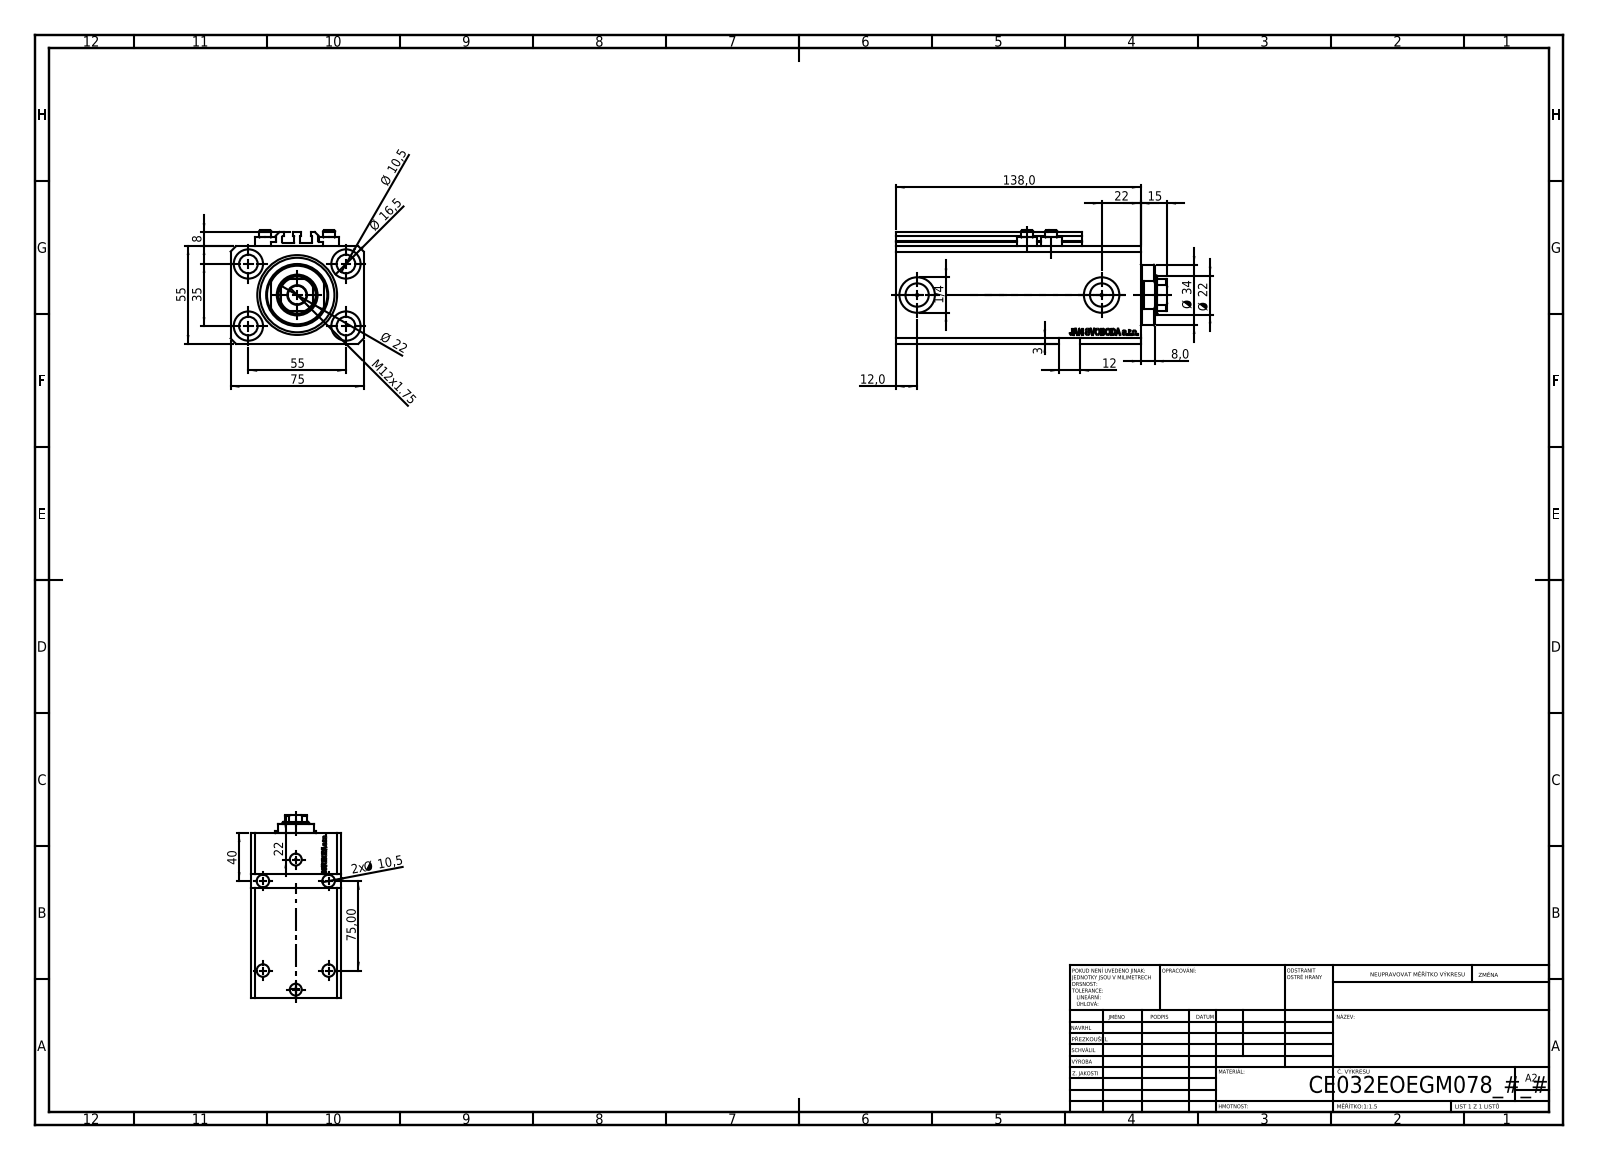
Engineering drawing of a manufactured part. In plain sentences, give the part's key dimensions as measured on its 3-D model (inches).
The part is named "V250CE_E_Body; V250CE_C_VCP; ALLEN BOLT V250CE; V250CE_VC_E". Its 3-D file was written by "SolidWorks 2019 (CONFIG_CONTROL_DESIGN)". It is 8 solids with 1084 faces: 514 planar, 146 cylindrical and 424 other. Overall it measures 6.024 by 2.953 by 2.52 inches. Its volume is 29.19 cubic inches and its surface area 176.6 square inches. Round holes: 9 of diameter 0.413, 4 of diameter 0.049, 4 of diameter 0.157, 4 of diameter 0.65, 2 of diameter 0.394, 2 of diameter 0.518, 2 of diameter 0.787, 1 of diameter 0.866, 1 of diameter 1.26, 1 of diameter 1.772. Round bosses or shafts: 4 of diameter 0.457, 4 of diameter 0.276, 1 of diameter 1.339. Partial cylindrical surfaces (rounded edges, fillets, slot ends): 10 of radius 0.008, 1 of radius 0.413. The main face-to-face distances are 2.165, 2.953, 0.591, 5.433, 4.843, 0.118, 0.39, 2.244, 4.453, 5.043. The hole center spacings are 1.283, 2.165, 0.535, 0.555, 1.016, 1.242, 1.253, 1.294.
